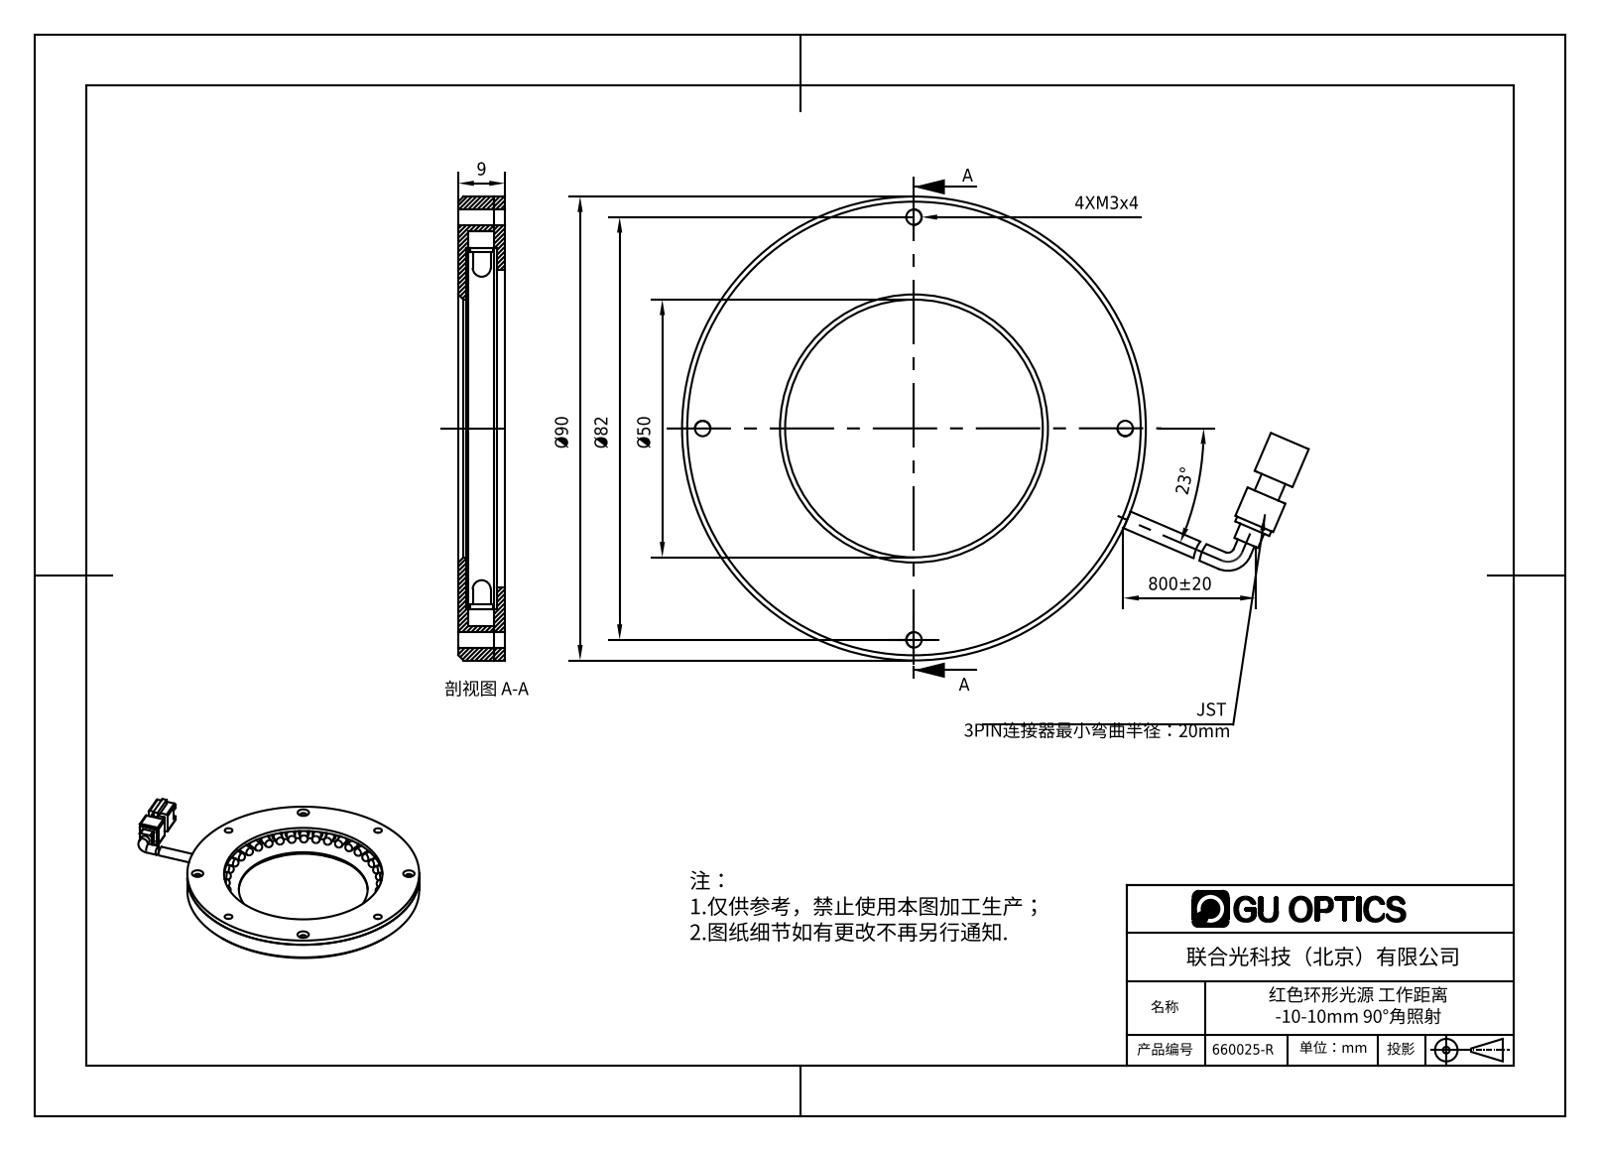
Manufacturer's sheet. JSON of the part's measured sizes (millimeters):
{"part_name": "660025-R", "step_written_by": "SolidWorks 2016 (AUTOMOTIVE_DESIGN)", "units": "millimeters", "bodies": {"solids": 45, "faces": 884, "planar": 553, "cylindrical": 267, "other": 64}, "overall_size": [121.62, 90, 10], "volume_mm3": 25302, "surface_area_mm2": 28044, "round_holes": [[3, 8], [1.6, 4], [2, 4], [2.4, 4], [3.5, 2], [50, 1], [61.48, 1], [69, 1], [70, 1], [76.68, 1]], "round_bosses_or_shafts": [[3.8, 40], [3, 40], [3.5, 2], [90, 1], [69.4, 1]], "partial_cylinders_radius": [[0.5, 8], [1, 4], [1.8, 2], [5, 1], [33.5, 1], [37.1, 1]], "face_to_face_distances": [7, 2, 9, 1.5, 5.5, 7.5, 0.5, 6, 5, 1], "hole_center_spacings": [75.76, 82, 31.38, 41, 57.98, 31.35, 31.41, 57.96]}
